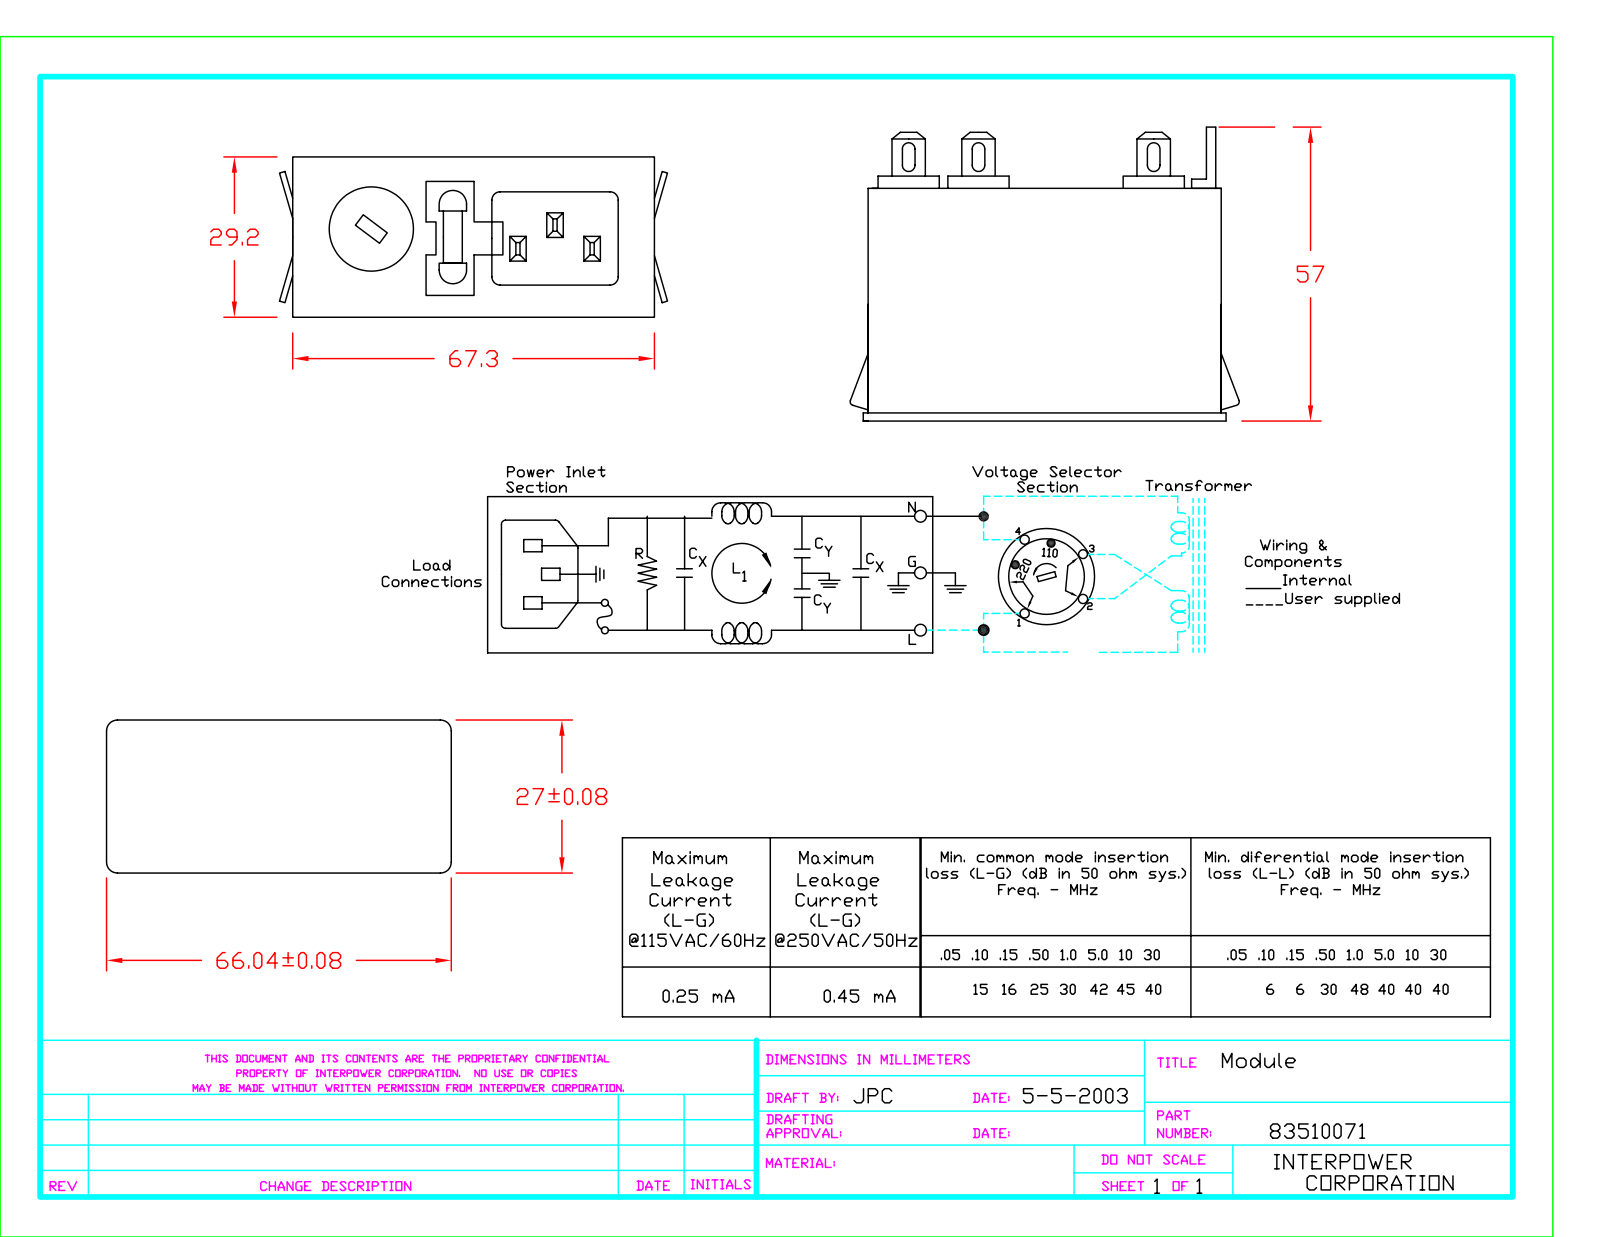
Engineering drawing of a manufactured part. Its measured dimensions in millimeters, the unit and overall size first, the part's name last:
Units: millimetres
Overall size (bounding box): 73.66 × 56.95 × 29.2
Round holes (diameter × count): ⌀2.01 ×4, ⌀2.97 ×2, ⌀11.81 ×1, ⌀16.41 ×1
Round bosses / shafts (diameter × count): ⌀15.91 ×1
Partial cylindrical surfaces — rounded edges, fillets, slot ends (radius × count): R0.25 ×16, R1.11 ×10, R0.38 ×8, R0.88 ×8, R1.11 ×4, R12.76 ×4, R13.01 ×4, R1 ×3
Main face-to-face distances: 27, 47.2, 65.2, 9.91, 1.8, 41.55, 33.81, 21.75, 23.9, 31.64
Hole centre spacings: 13.08, 29.8, 40.75, 41, 42.88
Volume: 78 135 mm³ · Surface area: 20 009 mm²
Bodies: 1 solid, 385 faces (292 planar, 85 cylindrical, 8 other)
Part name (STEP PRODUCT): 83510071
STEP written by: SolidWorks 2007 (CONFIG_CONTROL_DESIGN)
